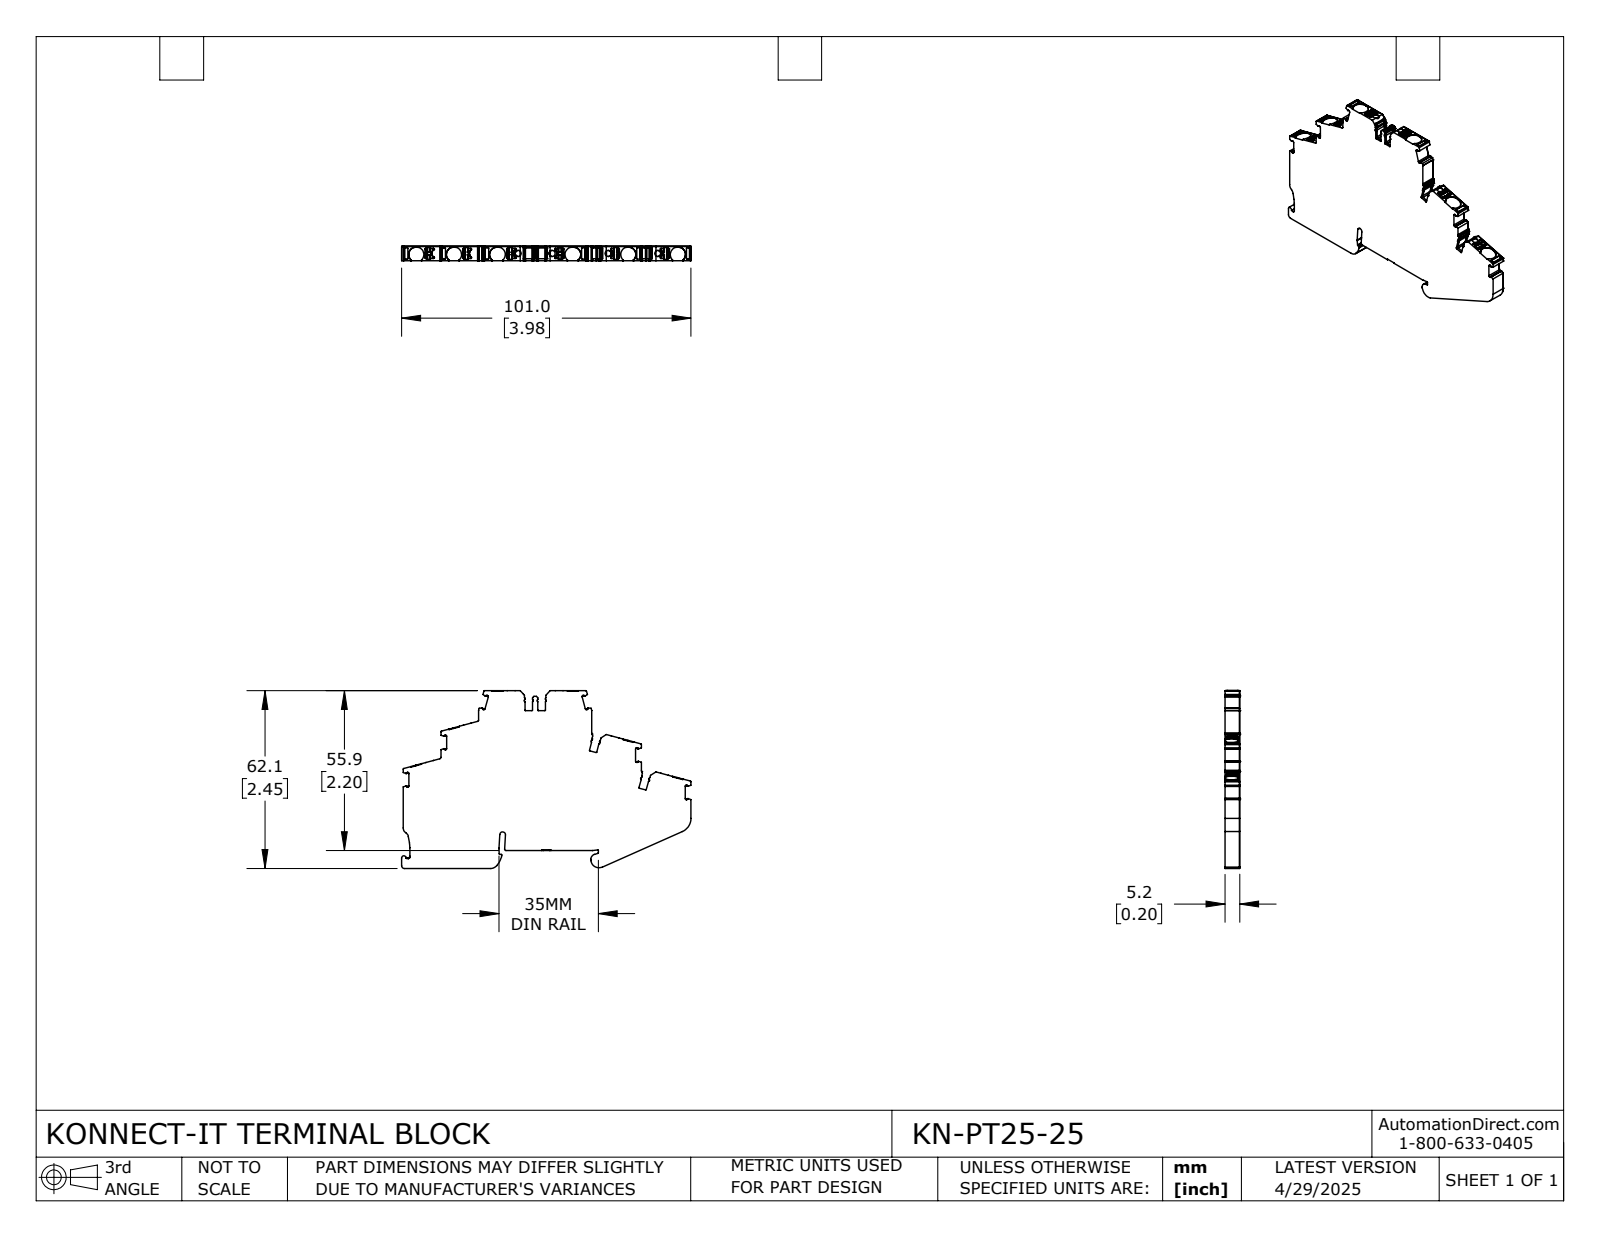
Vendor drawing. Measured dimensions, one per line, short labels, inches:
name: KN-PT25-25
written by: SolidWorks 2024 (CONFIG_CONTROL_DESIGN)
unit: in
bodies: 1 solid, 1212 faces (579 planar, 528 cylindrical, 105 other)
size: 3.977 × 2.445 × 0.203
volume: 1.354 in³; area: 16.76 in²
holes: 4× ⌀0.083
rounds: 128× R0.008, 49× R0.004, 47× R0.012, 26× R0.02, 24× R0.006, 17× R0.016, 14× R0.024, 12× R0.006
face distances: 0.203, 0.246, 0.079, 2.191, 2.437, 0.319, 0.682, 0.519, 2.445, 2.199
hole spacings: 0.466, 0.792
